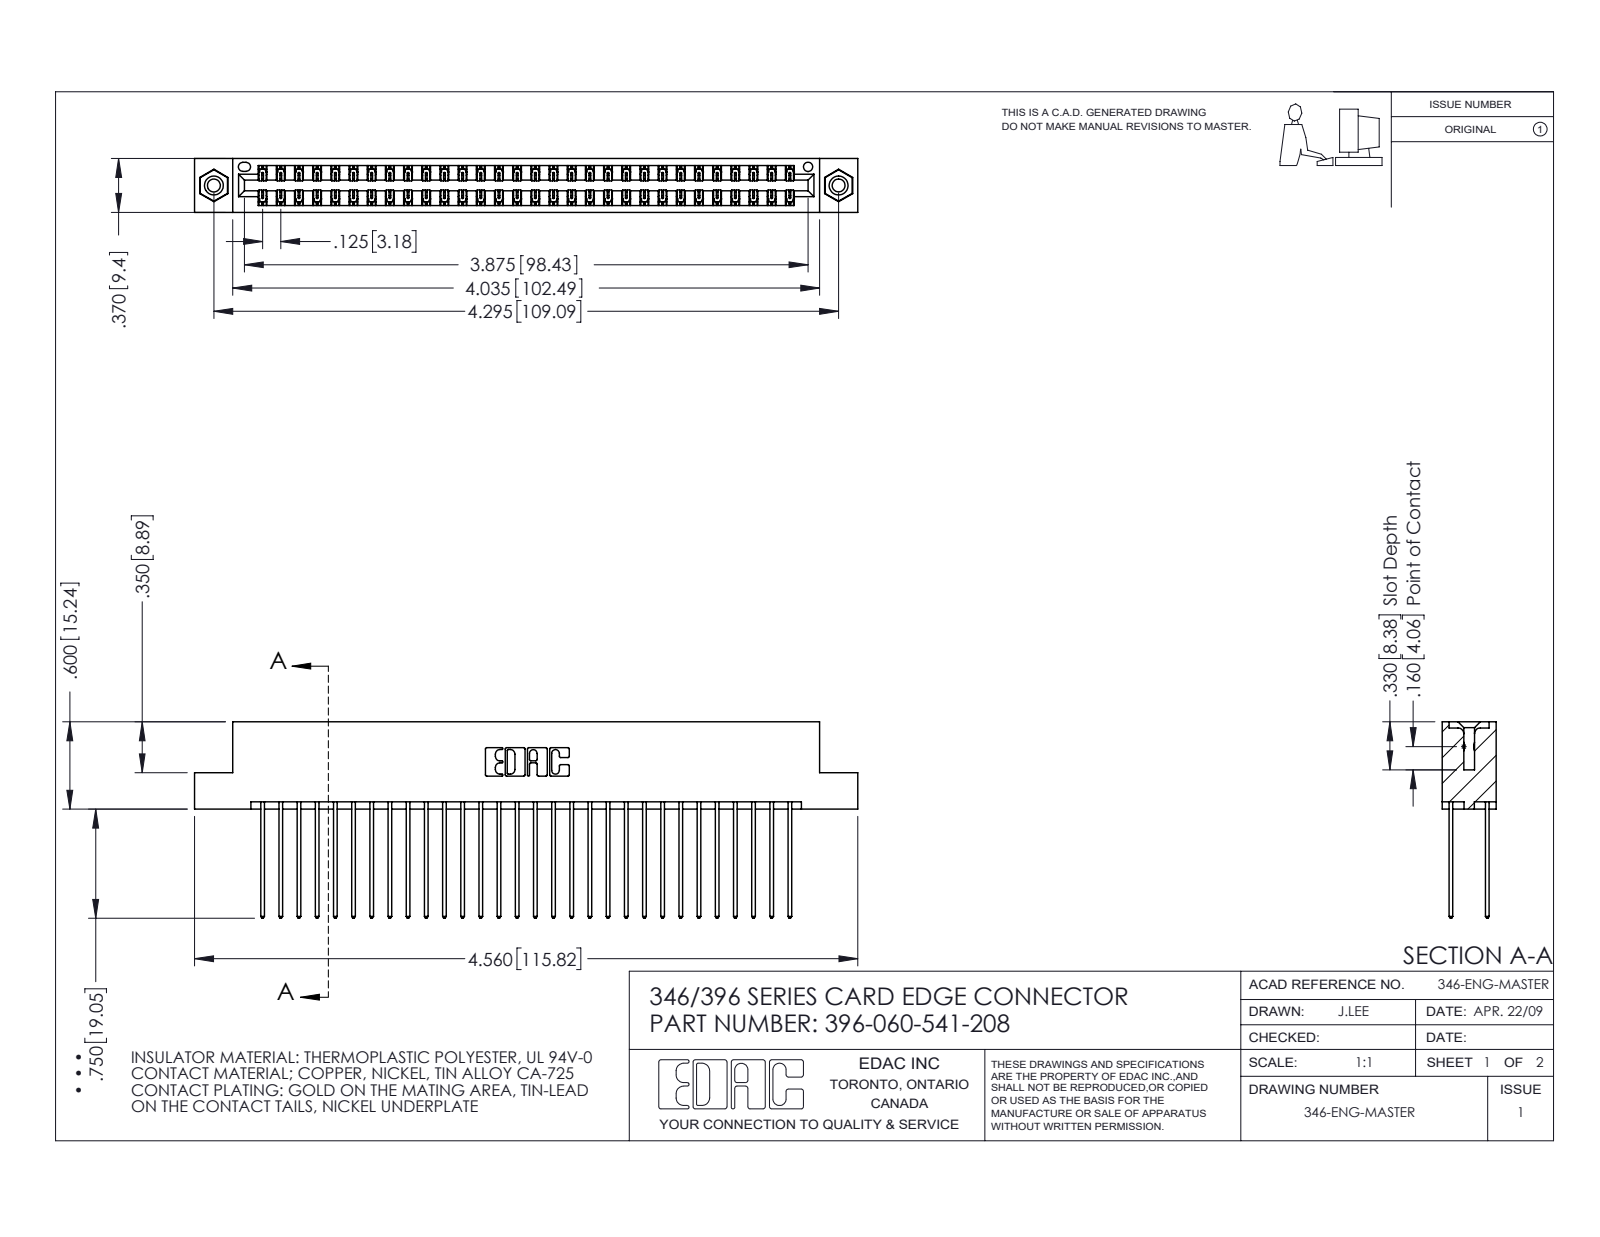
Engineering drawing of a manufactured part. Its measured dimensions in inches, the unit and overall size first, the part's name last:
Units: inches
Overall size (bounding box): 4.56 × 1.35 × 0.37
Round holes (diameter × count): ⌀0.089 ×2, ⌀0.125 ×2, ⌀0.156 ×2, ⌀0.064 ×1
Round bosses / shafts (diameter × count): ⌀0.155 ×2
Partial cylindrical surfaces — rounded edges, fillets, slot ends (radius × count): R0.006 ×90, R0.01 ×60, R0.01 ×22, R0.007 ×6, R0.031 ×6, R0.026 ×3, R0.014 ×2, R0.022 ×2
Main face-to-face distances: 0.048, 0.322, 0.25, 0.072, 0.298, 0.025, 0.37, 0.275, 0.225, 0.148
Hole centre spacings: 0.246, 4.087, 4.295
Volume: 0.704 in³ · Surface area: 26.88 in²
Bodies: 63 solids, 3302 faces (2208 planar, 1078 cylindrical, 16 other)
Part name (STEP PRODUCT): 345-250-001_345-250-003-102; 345-292-001_345-293-141; 346 Part_Flush Mounting Lugs - 0.156 Dia-TI; 396-060-541-208
STEP written by: SolidWorks 2016 (CONFIG_CONTROL_DESIGN)
